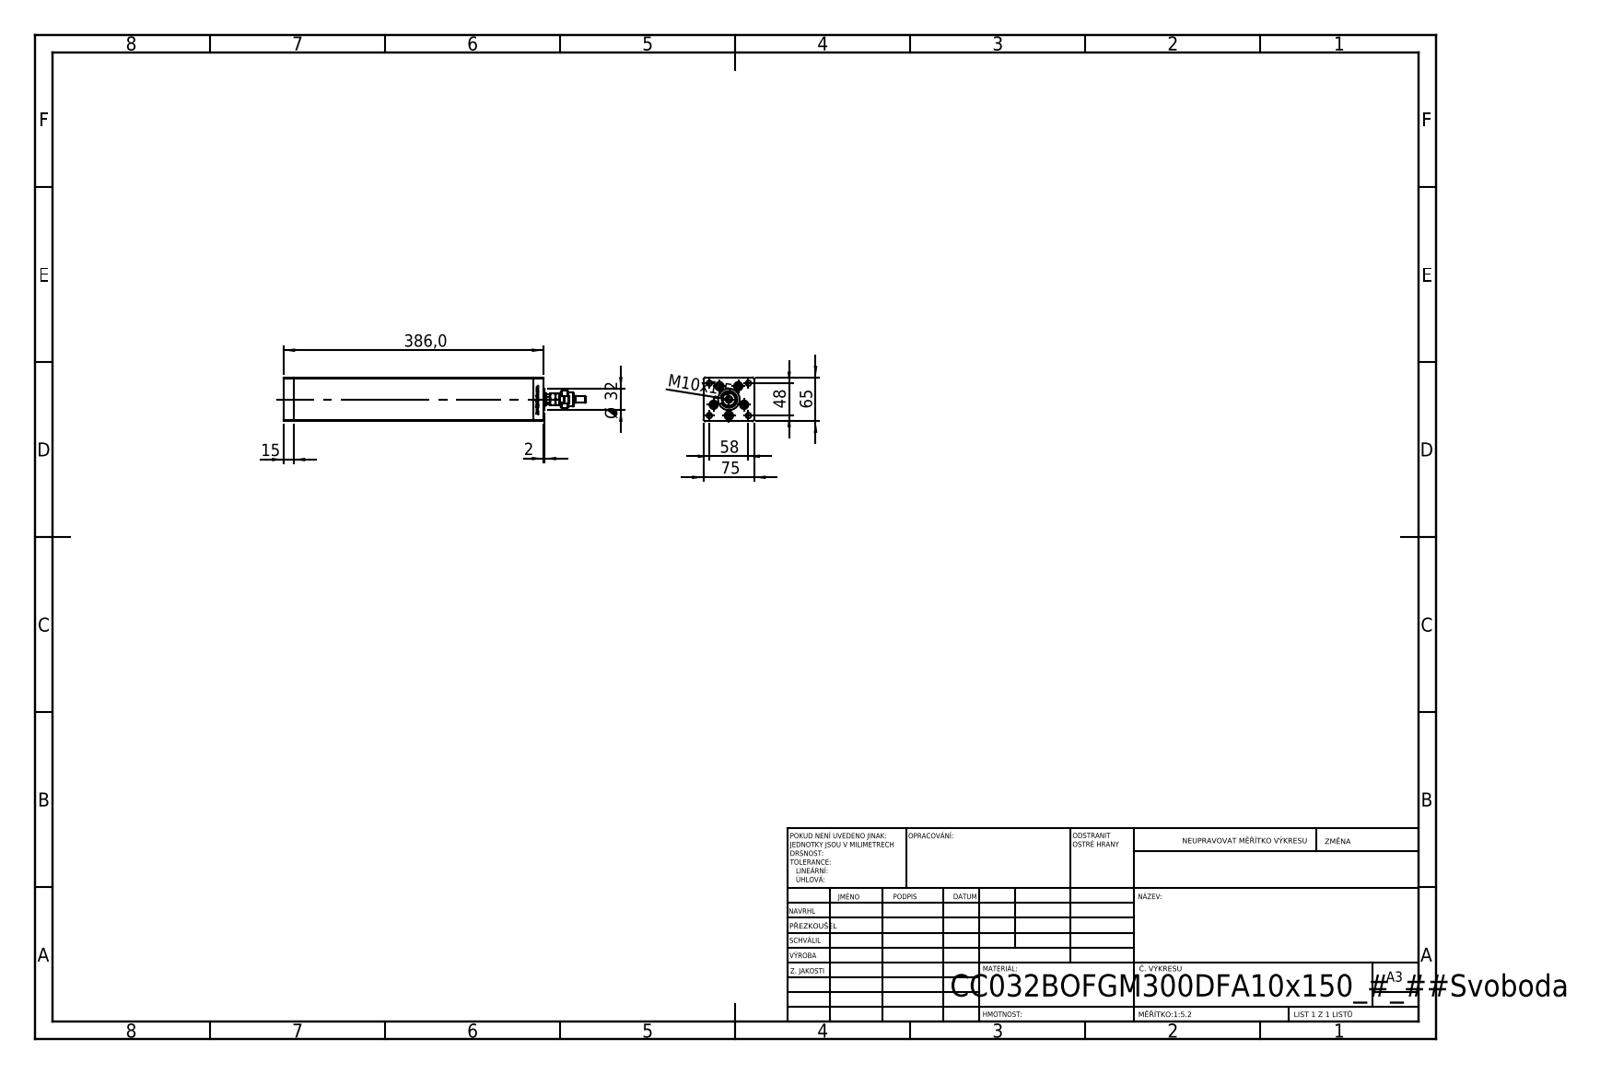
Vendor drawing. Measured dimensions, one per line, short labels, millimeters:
name: V220C_B MIDDLE; V220C_FRONT_B; FEMALE_PART_FOR_DFA; V220C_VC_B (+3 more)
written by: SolidWorks 2019 (CONFIG_CONTROL_DESIGN)
unit: mm
bodies: 16 solids, 1258 faces (488 planar, 152 cylindrical, 618 other)
size: 449 × 75 × 65
volume: 1 645 000 mm³; area: 232 076 mm²
holes: 5× ⌀9, 5× ⌀12.5, 4× ⌀8, 1× ⌀8.5, 1× ⌀18
bosses: 6× ⌀8, 1× ⌀32, 1× ⌀25, 1× ⌀21, 1× ⌀16, 1× ⌀10
rounds: 2× R0.93, 1× R5.5, 1× R8.5, 1× R8.75
face distances: 75, 65, 15, 356, 371, 54.5, 10.5, 26.25, 48.75, 6.5
hole spacings: 24, 37.64, 15.67, 17.22, 27.71, 28.83, 29, 32.63
